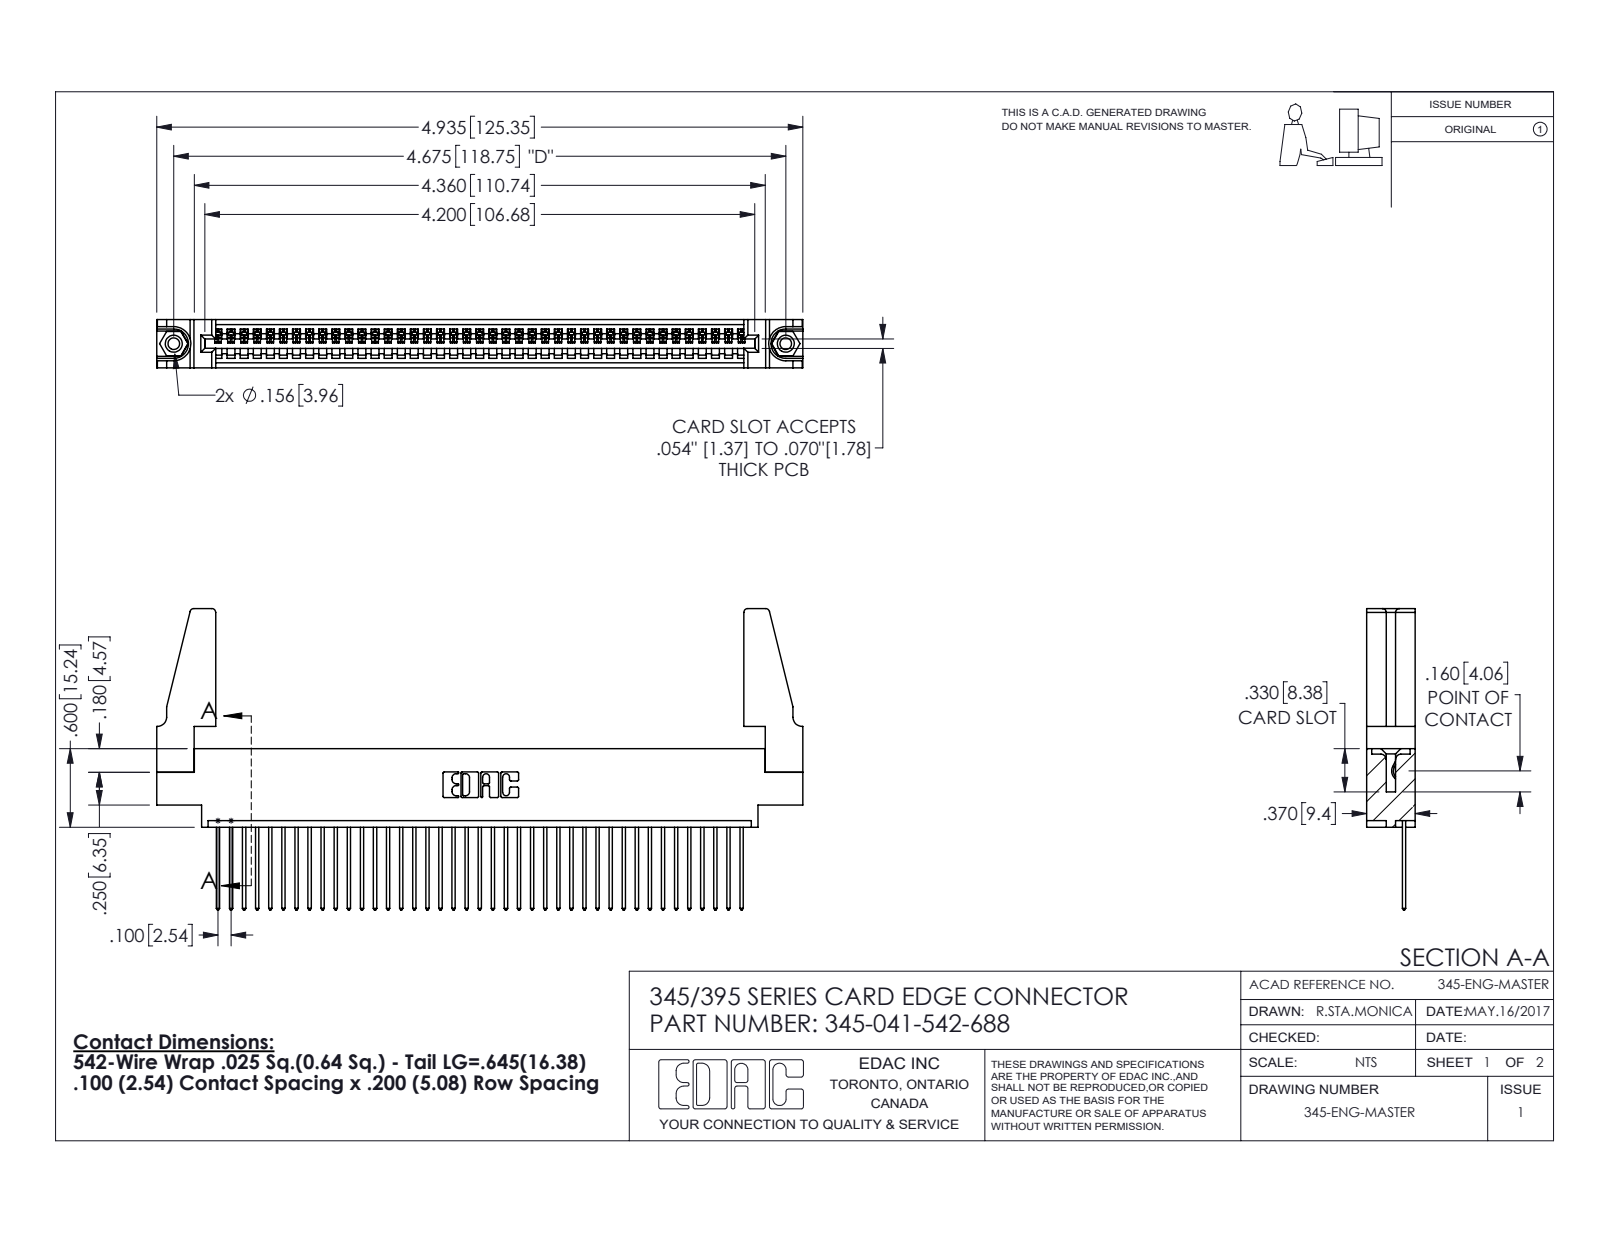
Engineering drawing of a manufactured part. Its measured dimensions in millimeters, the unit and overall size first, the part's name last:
Units: millimetres
Overall size (bounding box): 125.4 × 58.5 × 9.4
Round holes (diameter × count): ⌀2.3 ×2, ⌀3.2 ×2, ⌀4 ×2, ⌀1.6 ×1
Round bosses / shafts (diameter × count): ⌀3.9 ×2
Partial cylindrical surfaces — rounded edges, fillets, slot ends (radius × count): R0.2 ×82, R0.3 ×82, R0.3 ×22, R0.8 ×8, R0.2 ×6, R0.8 ×6, R0.7 ×3, R0.8 ×2
Main face-to-face distances: 1.8, 7.6, 9.4, 2.5, 6.9, 0.6, 5.1, 5.7, 4.4, 3.8
Hole centre spacings: 6.9, 112.8, 118.7
Volume: 15 100 mm³ · Surface area: 19 610 mm²
Bodies: 46 solids, 2632 faces (1796 planar, 820 cylindrical, 16 other)
Part name (STEP PRODUCT): 345-250-001_345-250-001-102; 345-220-078_345-220-088; 345-292-001_345-293-142; 345 Part_0.170 Offset - 0.156 Dia-TH (+1 more)
STEP written by: SolidWorks 2016 (CONFIG_CONTROL_DESIGN)
